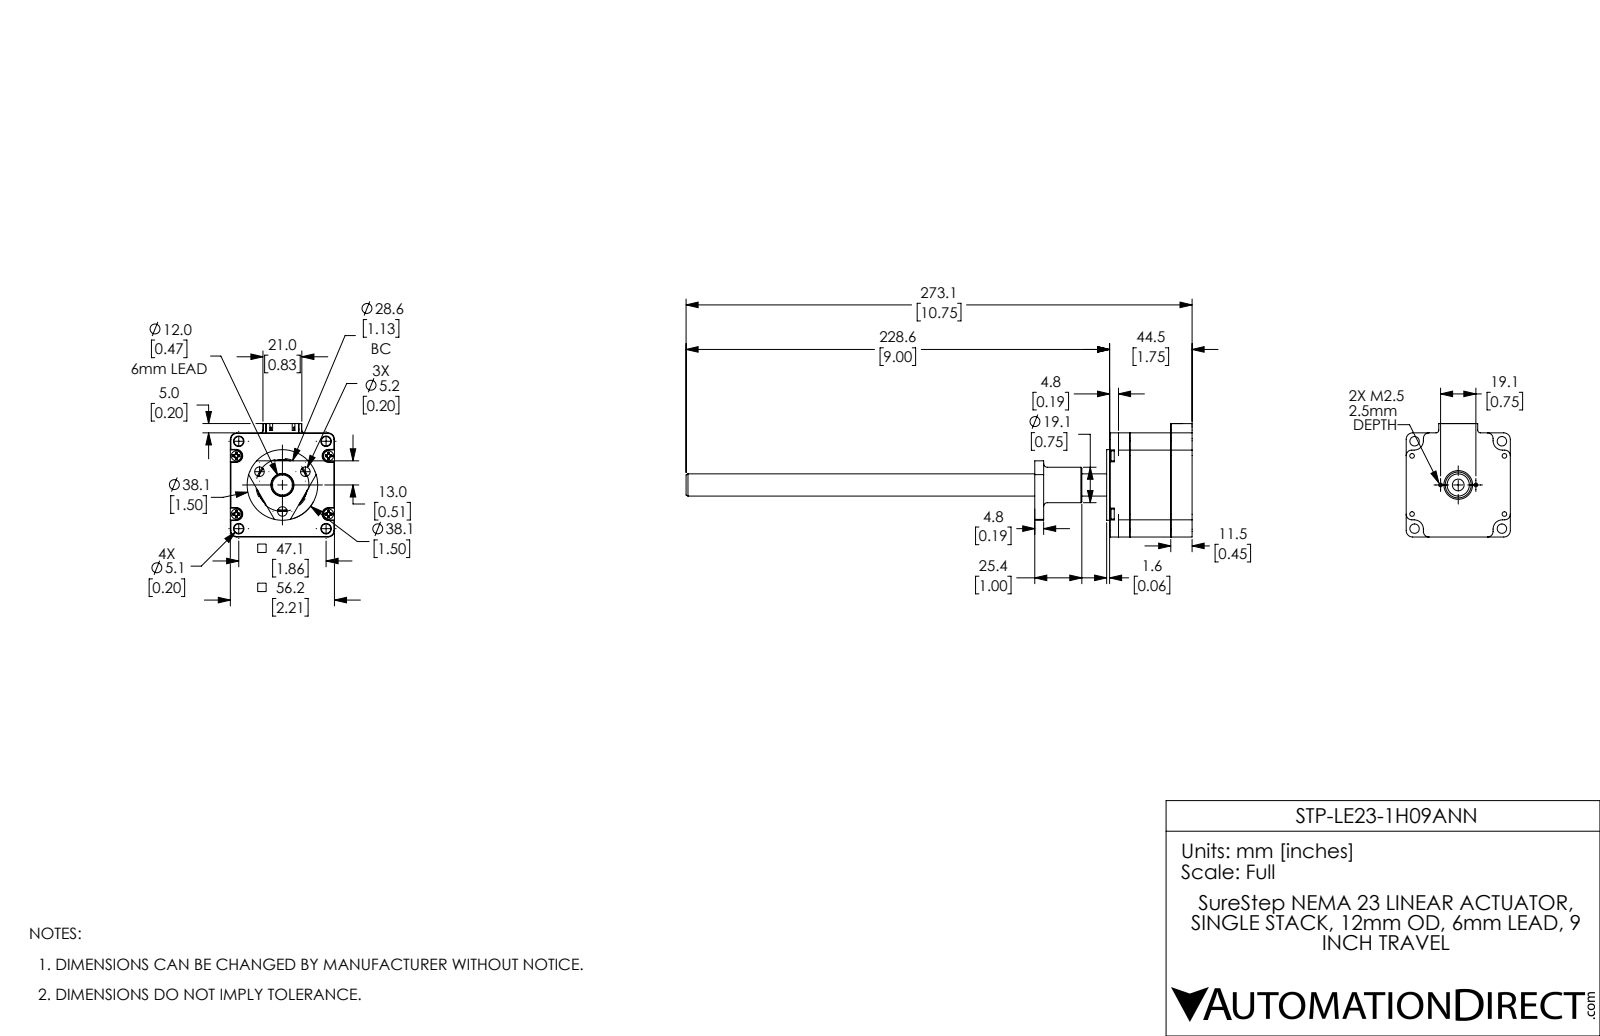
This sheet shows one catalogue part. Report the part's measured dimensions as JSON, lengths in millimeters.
{"part_name": "STP-LE23-1H09ANN_2; STP-LE23-1H09ANN_1; STP-LE23-1H09ANN", "step_written_by": "SolidWorks 2017 (AUTOMOTIVE_DESIGN)", "units": "millimeters", "bodies": {"solids": 8, "faces": 712, "planar": 282, "cylindrical": 199, "other": 231}, "overall_size": [273.1, 61.22, 56.2], "volume_mm3": 132789, "surface_area_mm2": 53025, "round_holes": [[4.5, 8], [2.5, 4], [3.3, 4], [5.1, 4], [5.16, 3], [2, 2], [2.05, 2], [6.35, 1], [6.8, 1], [10.5, 1], [15.5, 1], [20, 1]], "round_bosses_or_shafts": [[5.4, 4], [38.1, 1], [36, 1], [35.6, 1], [34.85, 1], [19.1, 1], [16, 1], [12, 1]], "partial_cylinders_radius": [[1.5, 10], [3, 8], [1.8, 4], [3.2, 4], [3.5, 4], [5, 4], [19.3, 1]], "face_to_face_distances": [22, 44.5, 56.2, 11.5, 33.5, 1.6, 51.4, 11, 33, 38.8], "hole_center_spacings": [14.12, 24.75, 33.05, 35.01, 45.74, 48.53, 56.99, 6.55]}
